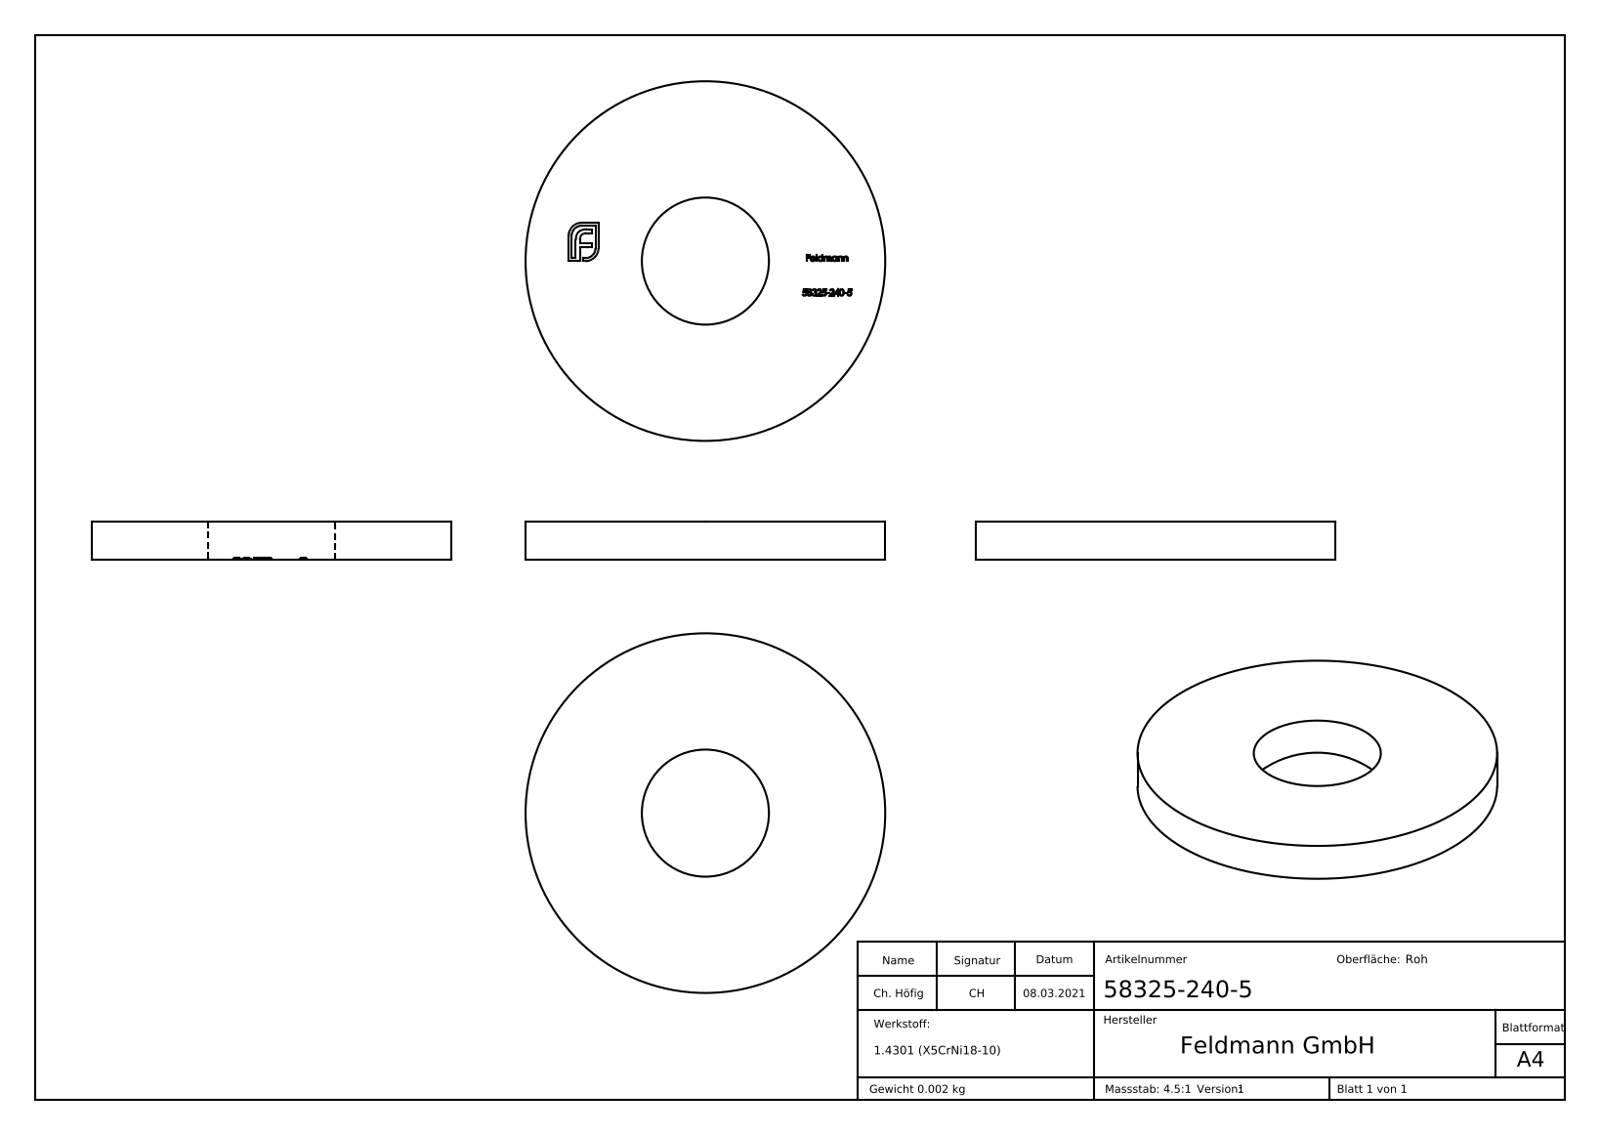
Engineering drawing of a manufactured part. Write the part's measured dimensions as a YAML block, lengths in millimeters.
part_name: "58325-240-5"
step_written_by: "SolidWorks 2018 (CONFIG_CONTROL_DESIGN)"
units: millimeters
bodies: {solids: 1, faces: 305, planar: 157, cylindrical: 4, other: 144}
overall_size: [15, 15, 1.6]
volume: 247
surface_area: 415
round_holes:
  - {diameter: 5.3, count: 1}
round_bosses_or_shafts:
  - {diameter: 15, count: 1}
face_to_face_distances: [1.6, 1.5, 1.12, 0.65, 1.47, 1.24, 1, 0.82, 0.58, 1.44]
